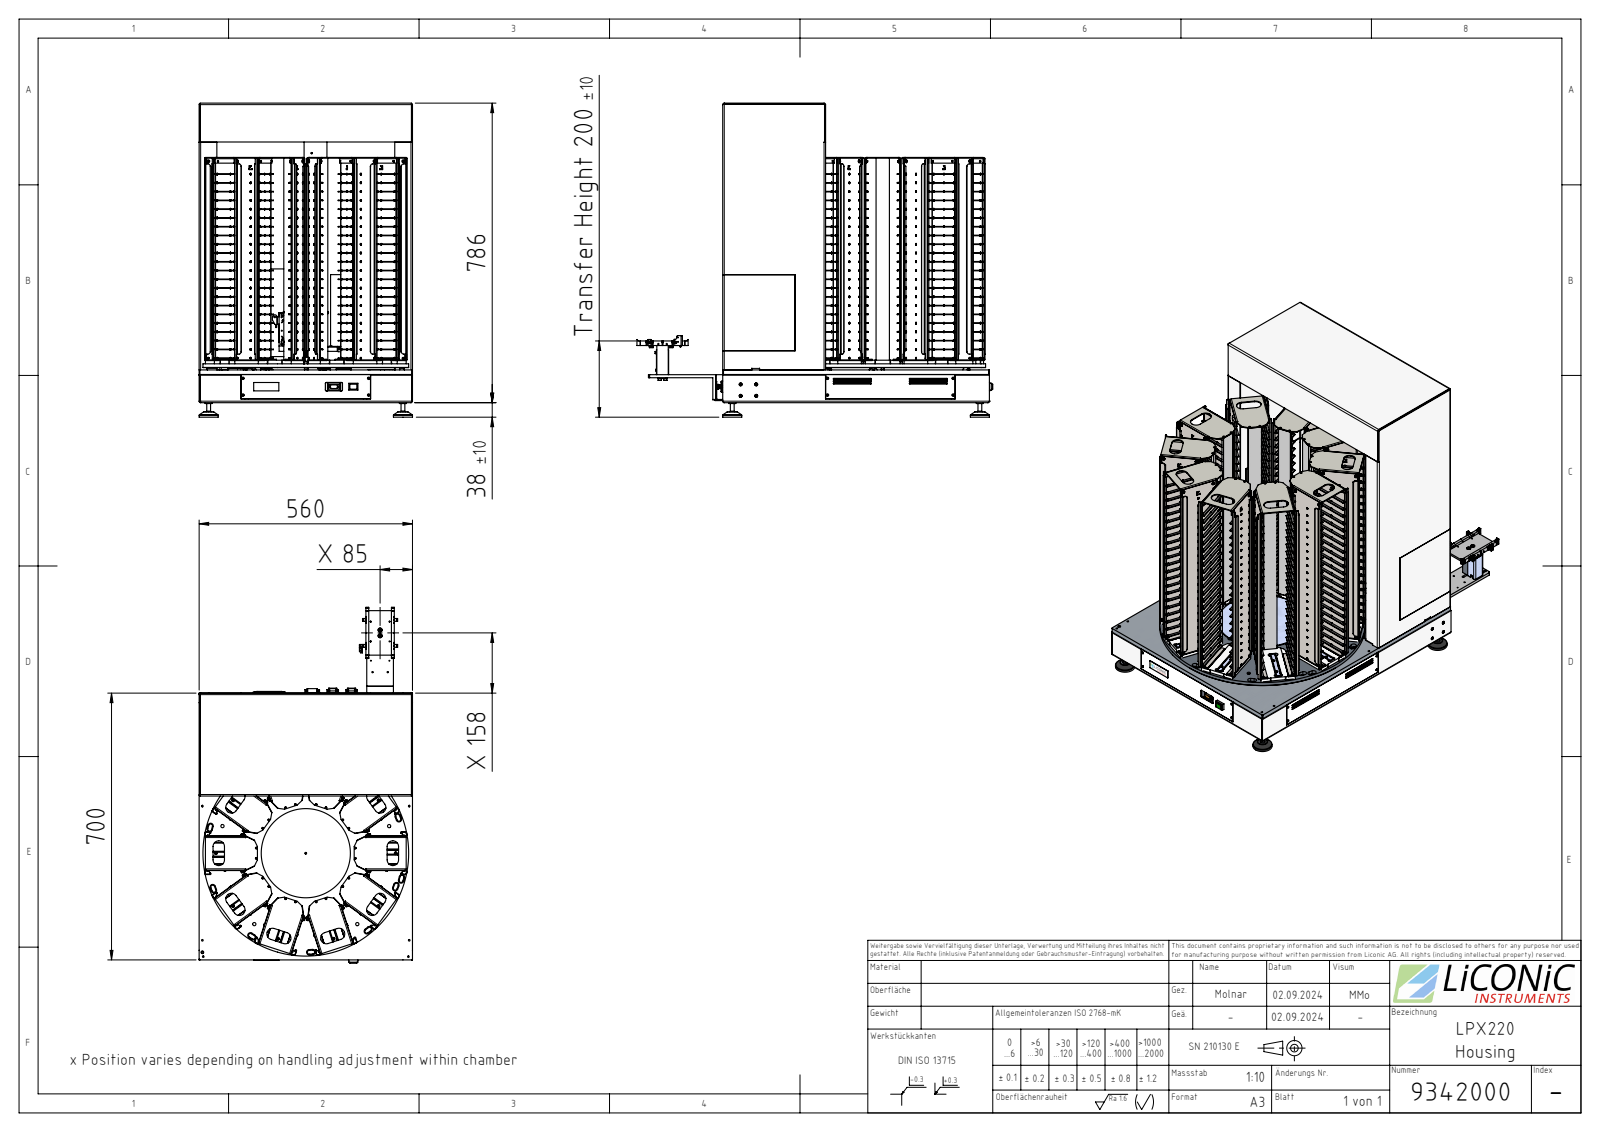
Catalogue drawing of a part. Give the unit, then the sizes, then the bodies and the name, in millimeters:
Units: millimetres
Overall size (bounding box): 933.98 × 824 × 560.01
Round holes (diameter × count): ⌀2.5 ×61, ⌀4.2 ×55, ⌀3.3 ×33, ⌀6.5 ×28, ⌀4 ×22, ⌀7.1 ×16, ⌀3.4 ×10, ⌀6.2 ×10, ⌀3.1 ×8, ⌀8 ×8, ⌀11 ×8, ⌀5.3 ×6
Round bosses / shafts (diameter × count): ⌀50.01 ×4, ⌀10 ×4, ⌀1.5 ×3, ⌀540 ×1, ⌀234 ×1, ⌀15.5 ×1, ⌀14.5 ×1
Partial cylindrical surfaces — rounded edges, fillets, slot ends (radius × count): R0.1 ×832, R0.25 ×832, R2 ×193, R5 ×121, R2.5 ×114, R1 ×55, R3 ×36, R1.5 ×26
Main face-to-face distances: 2, 558, 72, 74, 12, 90, 86, 84, 784, 6
Hole centre spacings: 41, 30, 50.8, 158.39, 85.72, 206.95, 270.38, 437.48
Volume: 10 800 000 mm³ · Surface area: 5 288 000 mm²
Bodies: 40 solids, 7313 faces (4064 planar, 3125 cylindrical, 124 other)
Part name (STEP PRODUCT): 9342000
STEP written by: SolidWorks 2022 (AUTOMOTIVE_DESIGN)
